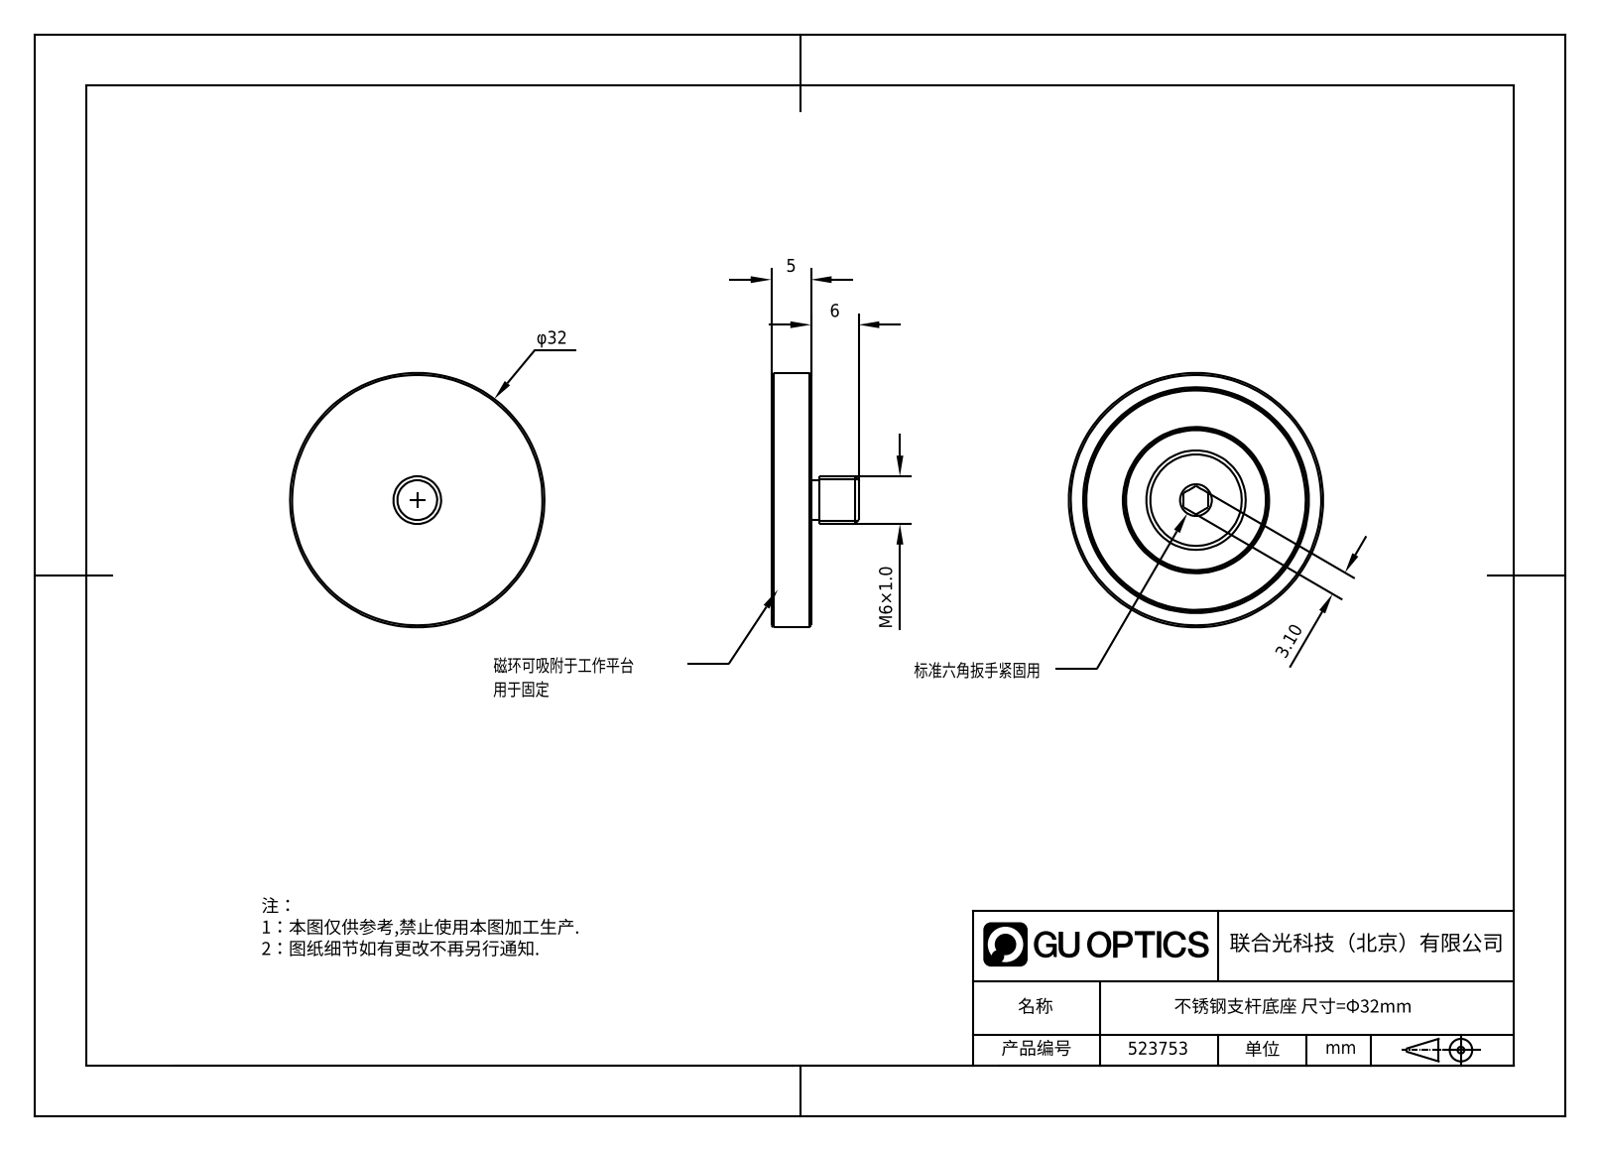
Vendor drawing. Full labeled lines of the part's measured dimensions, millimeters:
Part name (STEP PRODUCT): 1.4.6.1_ZGD-1.0B_1.0英寸支杆底座带M6x6mm螺丝，Rev.A
STEP written by: SolidWorks 2021 (CONFIG_CONTROL_DESIGN)
Units: millimetres
Bodies: 1 solid, 28 faces (12 planar, 6 cylindrical, 10 other)
Overall size (bounding box): 32 × 32 × 11
Volume: 4 091 mm³ · Surface area: 2 241 mm²
Round bosses / shafts (diameter × count): ⌀32 ×1, ⌀6 ×1, ⌀5 ×1
Main face-to-face distances: 5, 0.5, 4.5, 6, 11, 10.5, 3.1, 5.5, 1, 3.5
